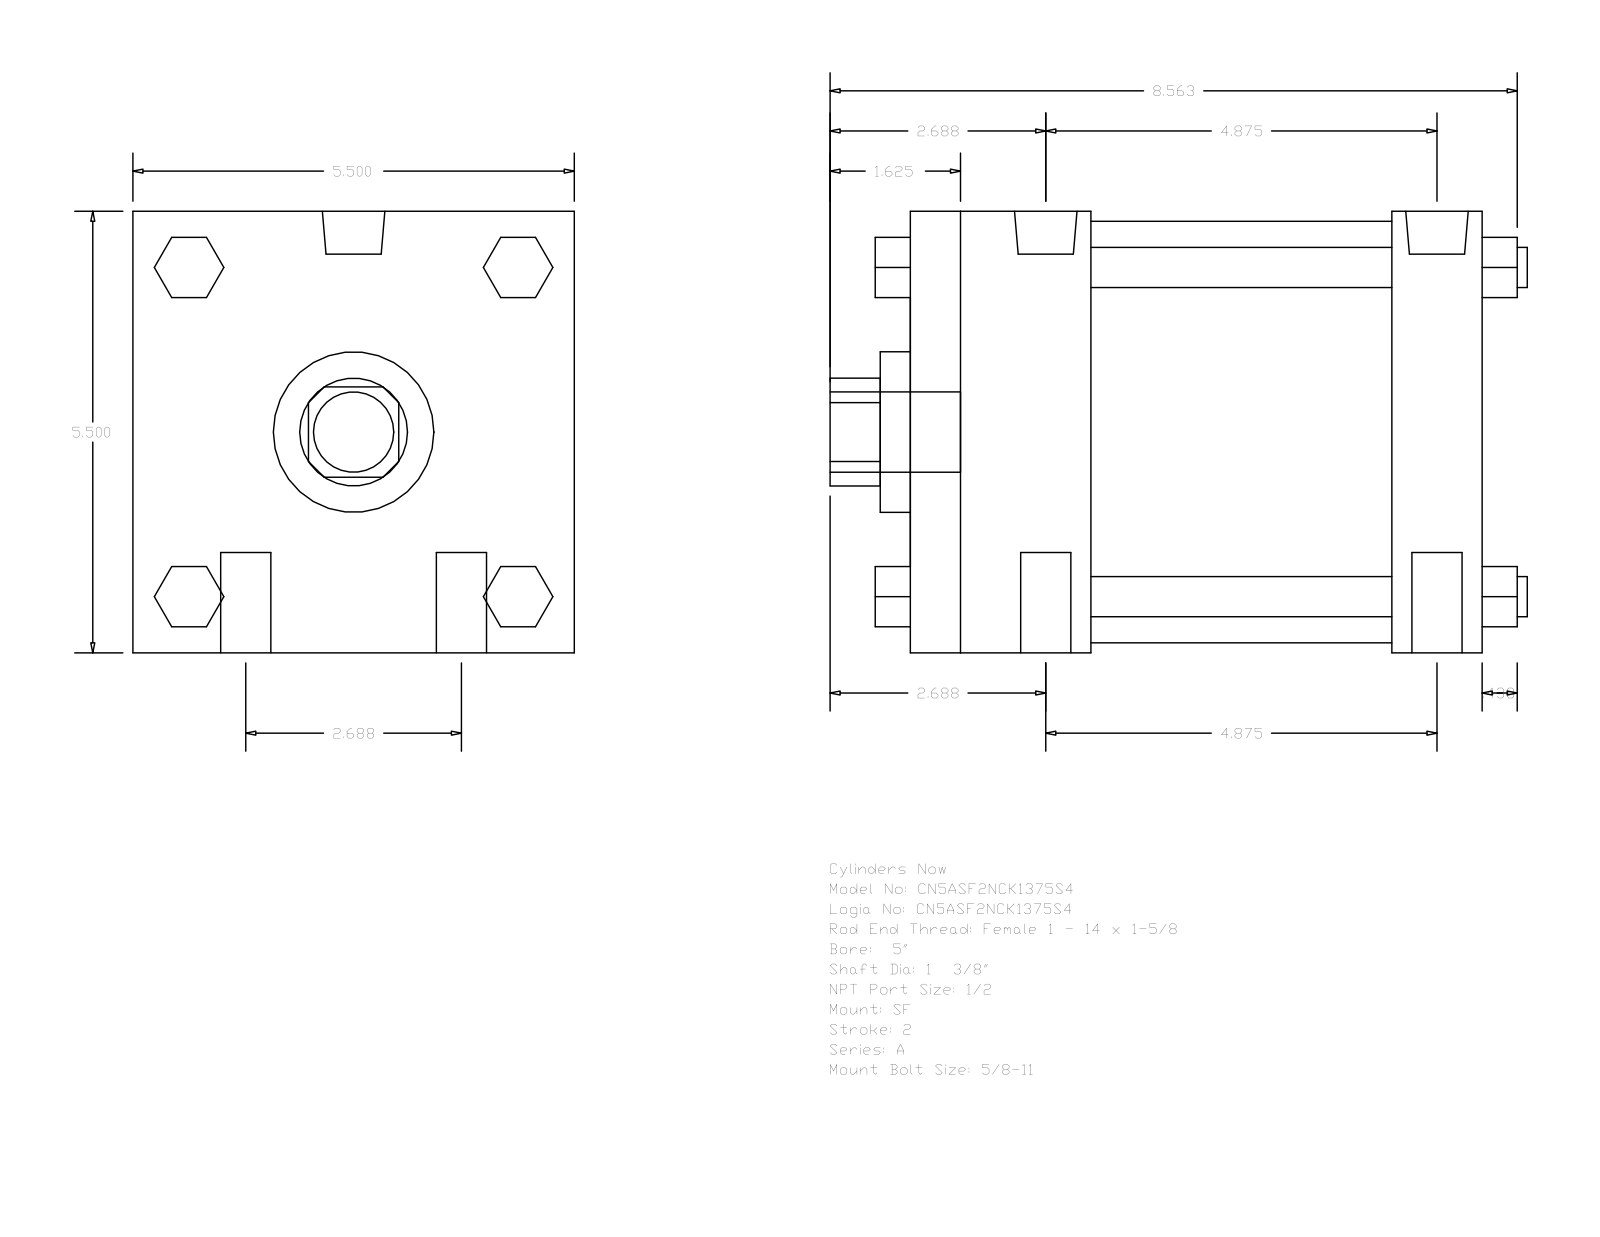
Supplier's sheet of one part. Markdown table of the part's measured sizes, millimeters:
| quantity | value |
| --- | --- |
| part name | A_SF__0500_1.375 |
| STEP written by | GSSL Pune (CONFIG_CONTROL_DESIGN) |
| units | millimeters |
| bodies | 0 solids, 124 faces (94 planar, 30 cylindrical, 0 other) |
| overall size | 220.66 × 139.7 × 139.7 |
| round holes (diameter × count) | 34.92 × 1, 50.8 × 1, 133.35 × 1 |
| round bosses / shafts (diameter × count) | 15.88 × 4, 12.7 × 4, 19.77 × 2, 8.73 × 2, 25.4 × 1 |
| partial cylindrical surfaces (radius × count) | 17.06 × 1 |
| main face-to-face distances | 139.7, 180.98, 28.58, 57.15, 152.4, 95.25, 123.83, 19.05, 52.07, 90.18 |
